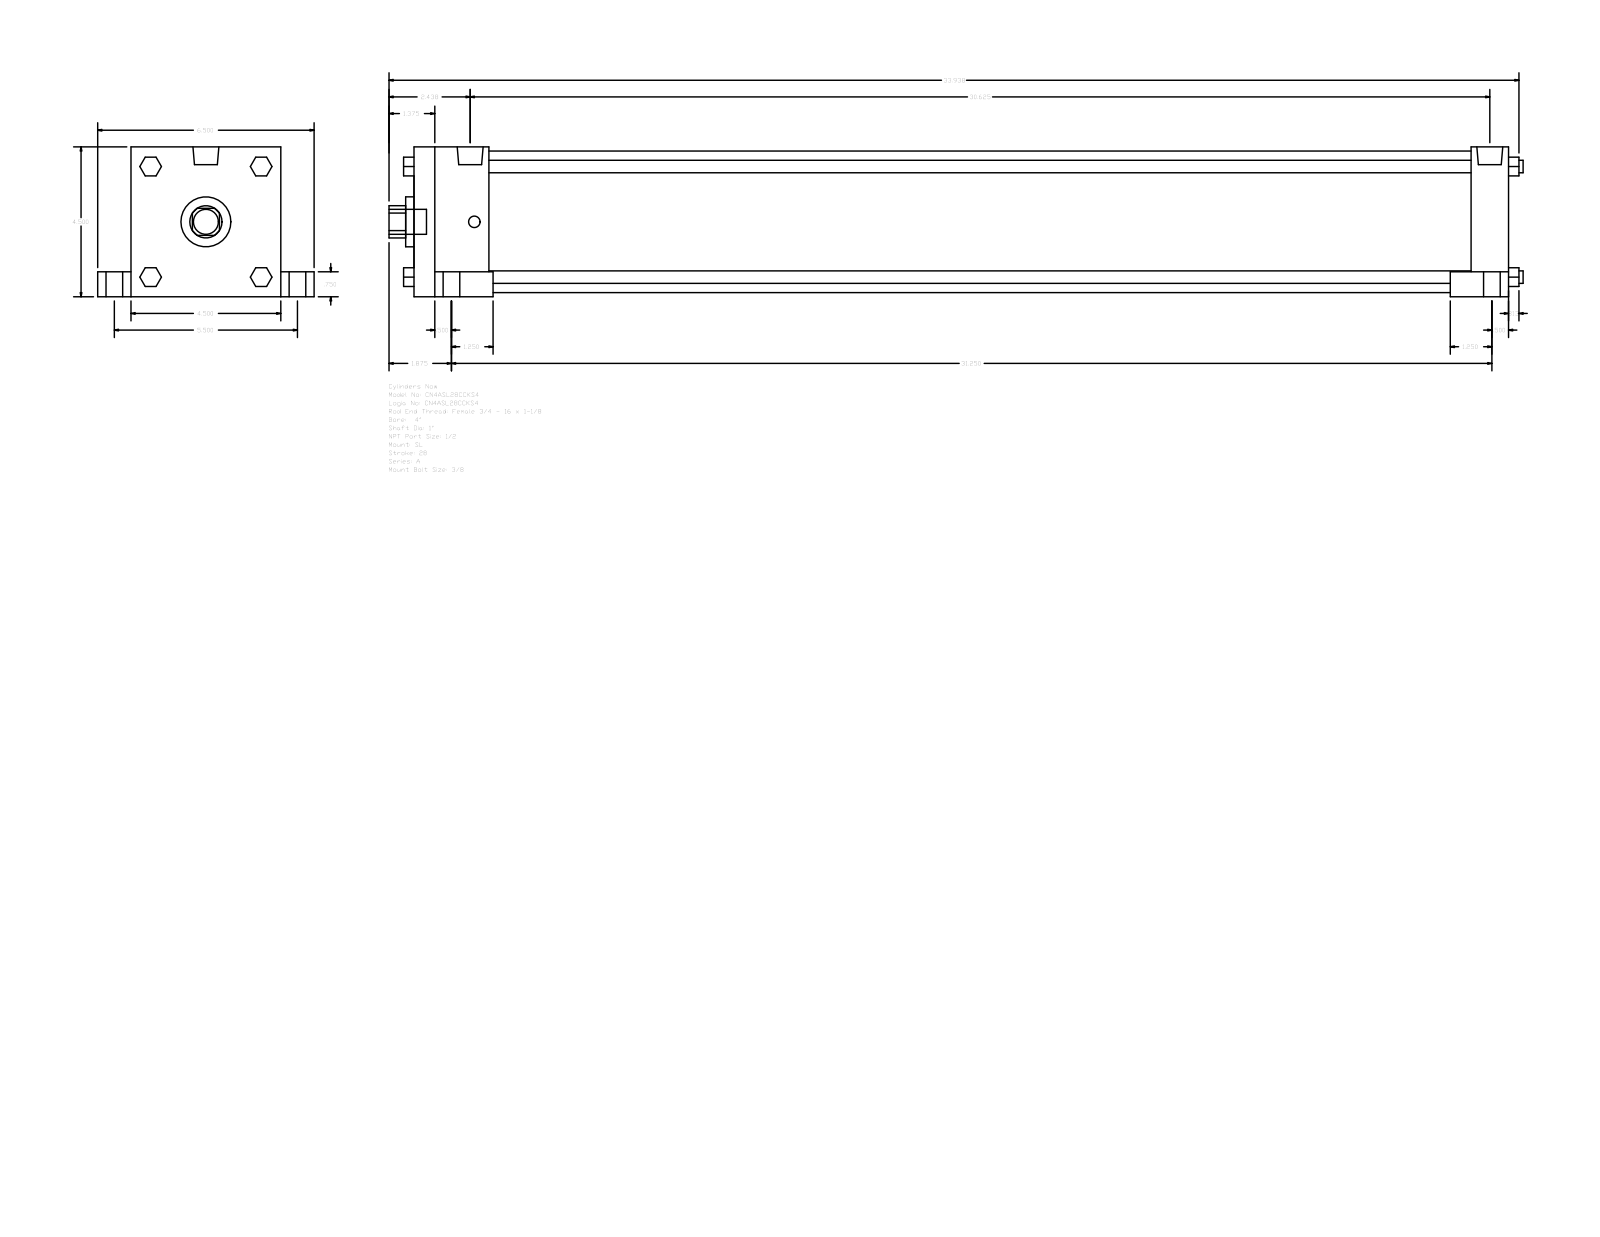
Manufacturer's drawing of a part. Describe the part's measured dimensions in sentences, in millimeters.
The part is named "A_SL__0400_1". Its 3-D file was written by "GSSL Pune (CONFIG_CONTROL_DESIGN)". It is 0 solids with 150 faces: 114 planar, 36 cylindrical and 0 other. Overall it measures 865.19 by 165.1 by 114.3 millimeters. Round holes: 1 of diameter 25.4, 1 of diameter 38.1, 1 of diameter 107.95. Round bosses or shafts: 5 of diameter 19.05, 4 of diameter 12.7, 4 of diameter 9.53, 4 of diameter 8.73, 2 of diameter 19.77. Partial cylindrical surfaces (rounded edges, fillets, slot ends): 1 of radius 12.29. The main face-to-face distances are 114.3, 835.03, 57.15, 777.88, 806.45, 749.3, 28.58, 19.05, 25.4, 139.7.
